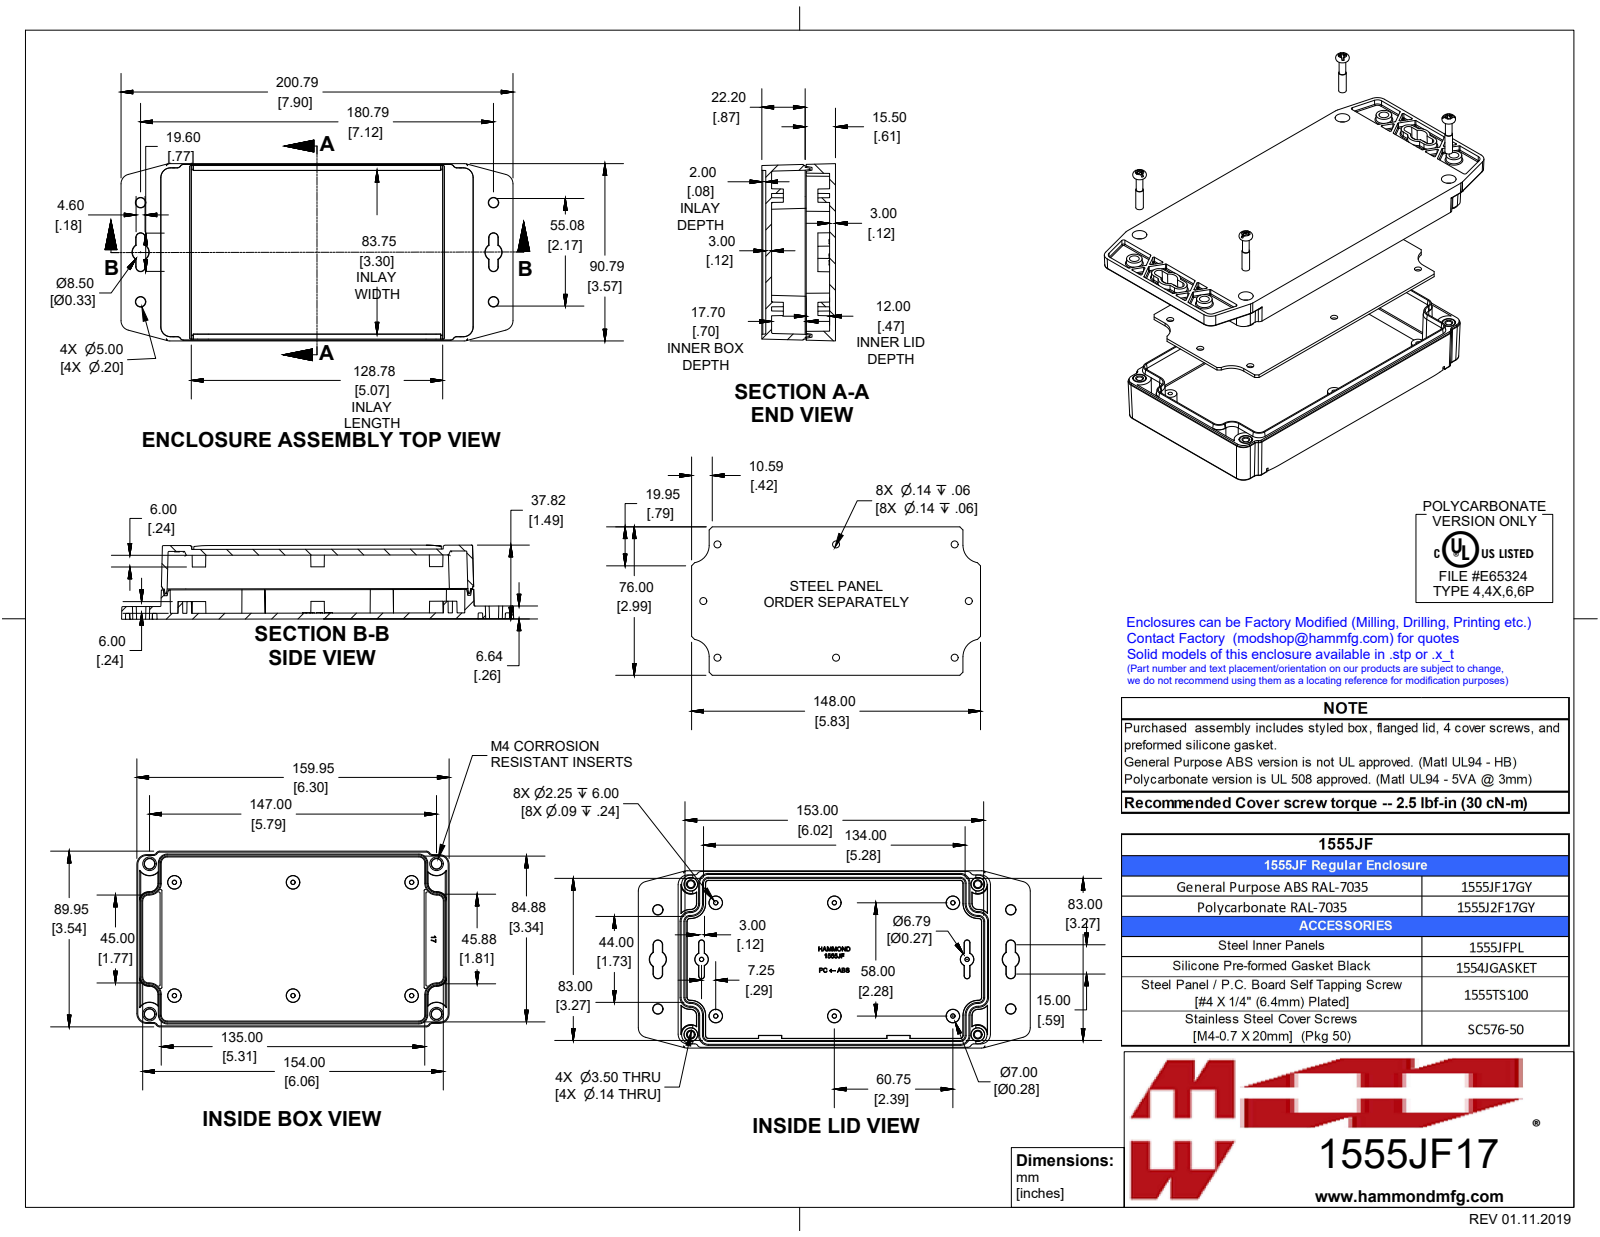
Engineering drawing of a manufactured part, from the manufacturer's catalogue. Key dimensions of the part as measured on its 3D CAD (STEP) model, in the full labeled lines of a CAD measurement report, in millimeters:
Part name (STEP PRODUCT): 1555J2F17GY
STEP written by: SolidWorks 2019 (CONFIG_CONTROL_DESIGN)
Units: millimetres
Bodies: 10 solids, 1324 faces (624 planar, 226 cylindrical, 474 other)
Overall size (bounding box): 200.8 × 90.8 × 37.7
Volume: 166 300 mm³ · Surface area: 115 900 mm²
Round holes (diameter × count): ⌀3.3 ×4, ⌀3.5 ×4, ⌀7 ×4
Round bosses / shafts (diameter × count): ⌀6.4 ×4, ⌀5.5 ×4, ⌀5.3 ×4, ⌀3.9 ×4, ⌀3.4 ×4
Partial cylindrical surfaces — rounded edges, fillets, slot ends (radius × count): R0.5 ×104, R5 ×16, R2.3 ×4, R4.7 ×4, R50.5 ×1, R51.2 ×1, R54 ×1, R54.1 ×1
Main face-to-face distances: 3, 32.7, 35.7, 29.7, 2, 34.7, 3.5, 6.5, 3, 5
Hole centre spacings: 77, 147, 165.9
